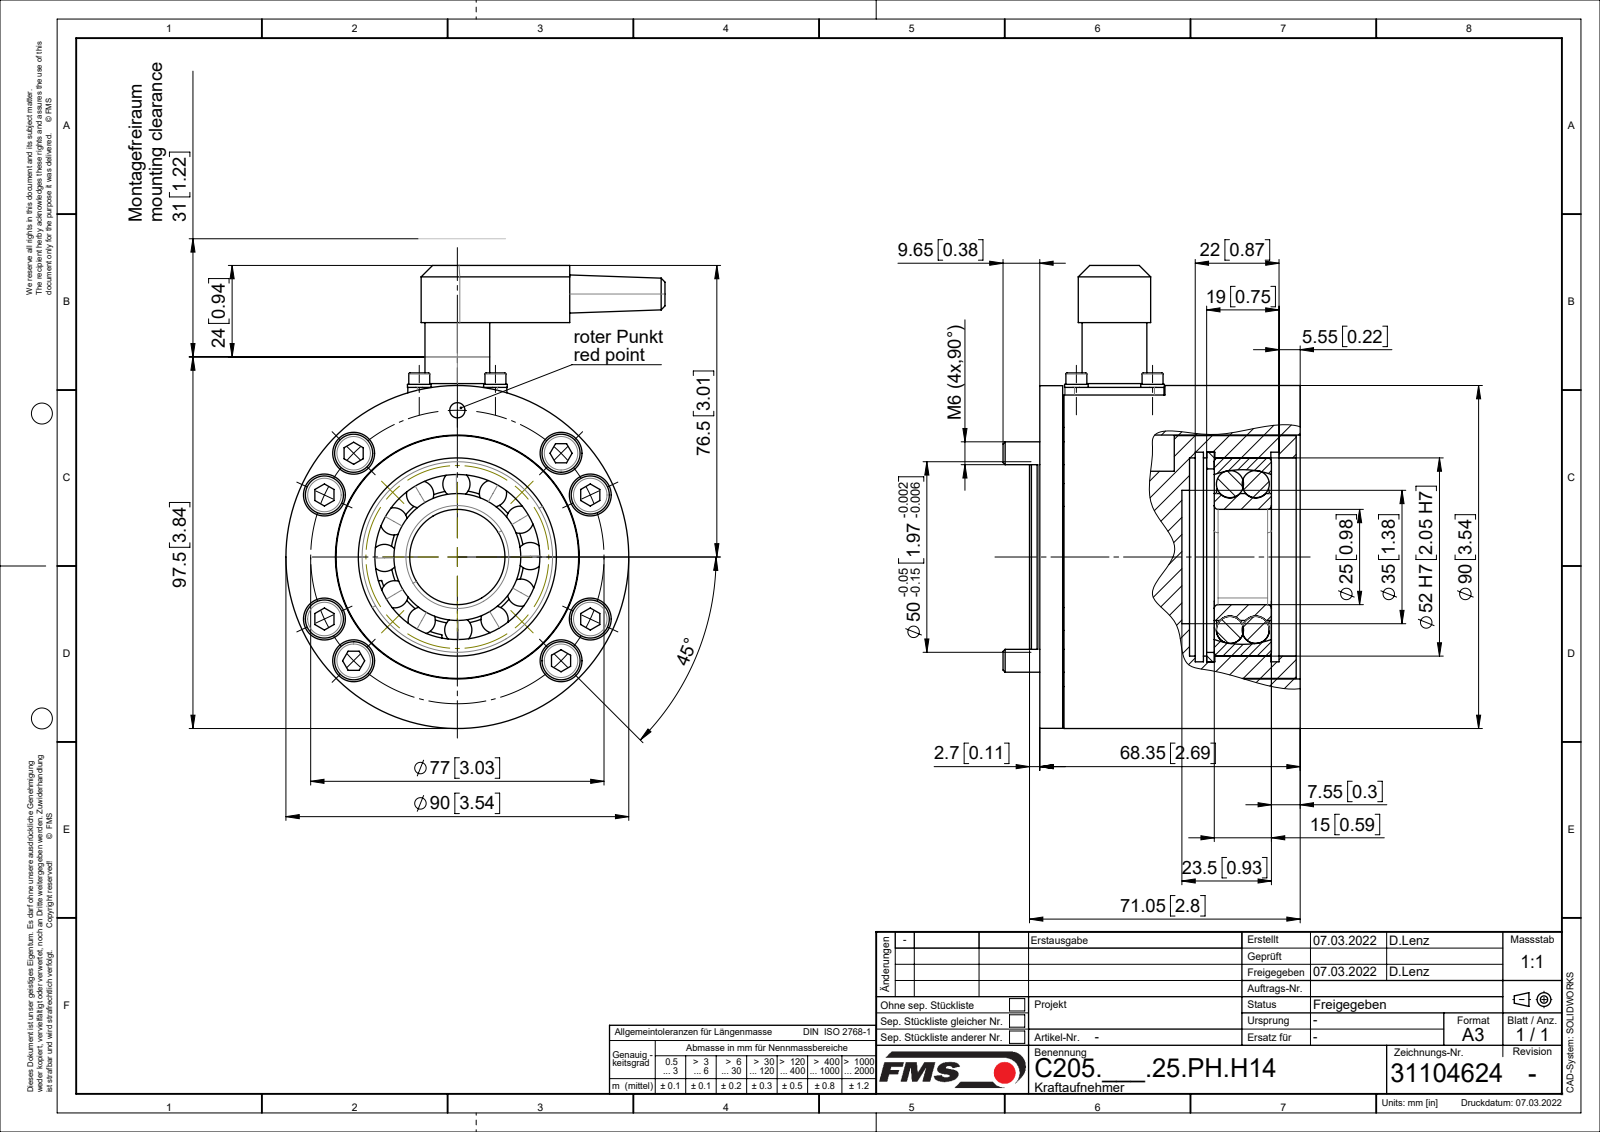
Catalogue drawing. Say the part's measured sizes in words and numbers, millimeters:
The part is named "Si-Ring DIN472_D52x2; 31104486_stp_nach_Vergueten; 31104484_Stp_01; Zyl-Schr DIN912_M6x40 (+8 more)". Its 3-D file was written by "SolidWorks 2018 (CONFIG_CONTROL_DESIGN)". It is 48 solids with 648 faces: 214 planar, 267 cylindrical and 167 other. Overall it measures 121.5 by 99.5 by 78 millimeters. Its volume is 310 090 cubic millimeters and its surface area 125 511 square millimeters. Round holes: 8 of diameter 6.5, 8 of diameter 11, 6 of diameter 2.5, 5 of diameter 2, 4 of diameter 3.1, 4 of diameter 3.2, 4 of diameter 5, 4 of diameter 7, 2 of diameter 4, 1 of diameter 10.2, 1 of diameter 12, 1 of diameter 15. Round bosses or shafts: 8 of diameter 10, 8 of diameter 6, 5 of diameter 1.5, 4 of diameter 6.2, 4 of diameter 5.5, 4 of diameter 3, 1 of diameter 90, 1 of diameter 89.9. Partial cylindrical surfaces (rounded edges, fillets, slot ends): 4 of radius 0.1, 4 of radius 2.5, 2 of radius 4.24, 2 of radius 5, 1 of radius 9.5, 1 of radius 20.8, 1 of radius 24.1. The main face-to-face distances are 6, 3.3, 32, 2.7, 6.5, 2, 33.05, 38, 30, 29.3. The hole center spacings are 20, 38.5, 13.37, 14.14, 38.49, 44.16, 54.44, 63.07.
